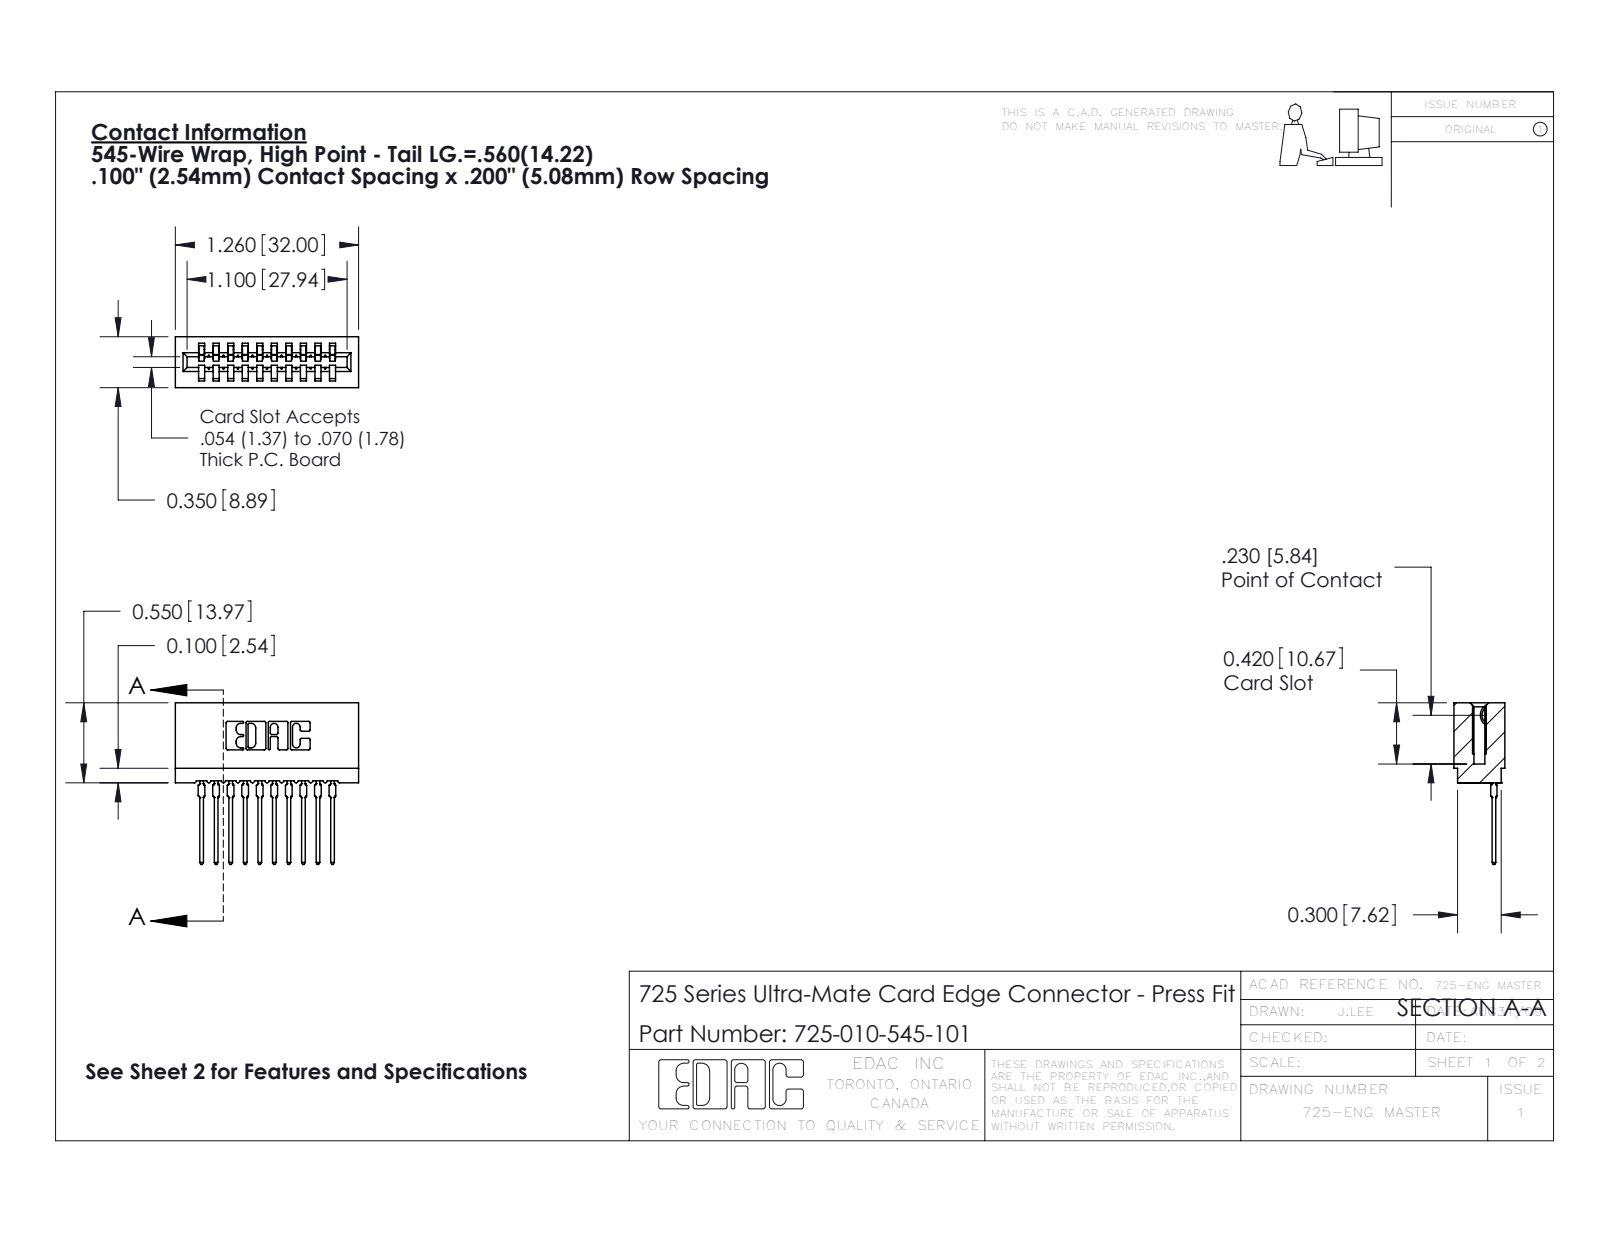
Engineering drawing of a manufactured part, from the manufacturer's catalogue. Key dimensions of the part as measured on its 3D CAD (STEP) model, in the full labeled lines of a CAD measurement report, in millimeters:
Part name (STEP PRODUCT): 725-010-545-101; 725 Part_Insulator Option - 01; 745-292-001_545
STEP written by: SolidWorks 2016 (CONFIG_CONTROL_DESIGN)
Units: millimetres
Bodies: 11 solids, 1215 faces (725 planar, 230 cylindrical, 260 other)
Overall size (bounding box): 32 × 28.2 × 8.9
Volume: 2 640 mm³ · Surface area: 4 641 mm²
Partial cylindrical surfaces — rounded edges, fillets, slot ends (radius × count): R0.3 ×22, R0.4 ×20, R0.5 ×20, R0.2 ×6, R0.8 ×6, R0.1 ×4, R0.3 ×4, R0.7 ×3
Main face-to-face distances: 2.5, 5.1, 7.6, 10.2, 1.1, 12.7, 3.6, 1.5, 6.1, 4
